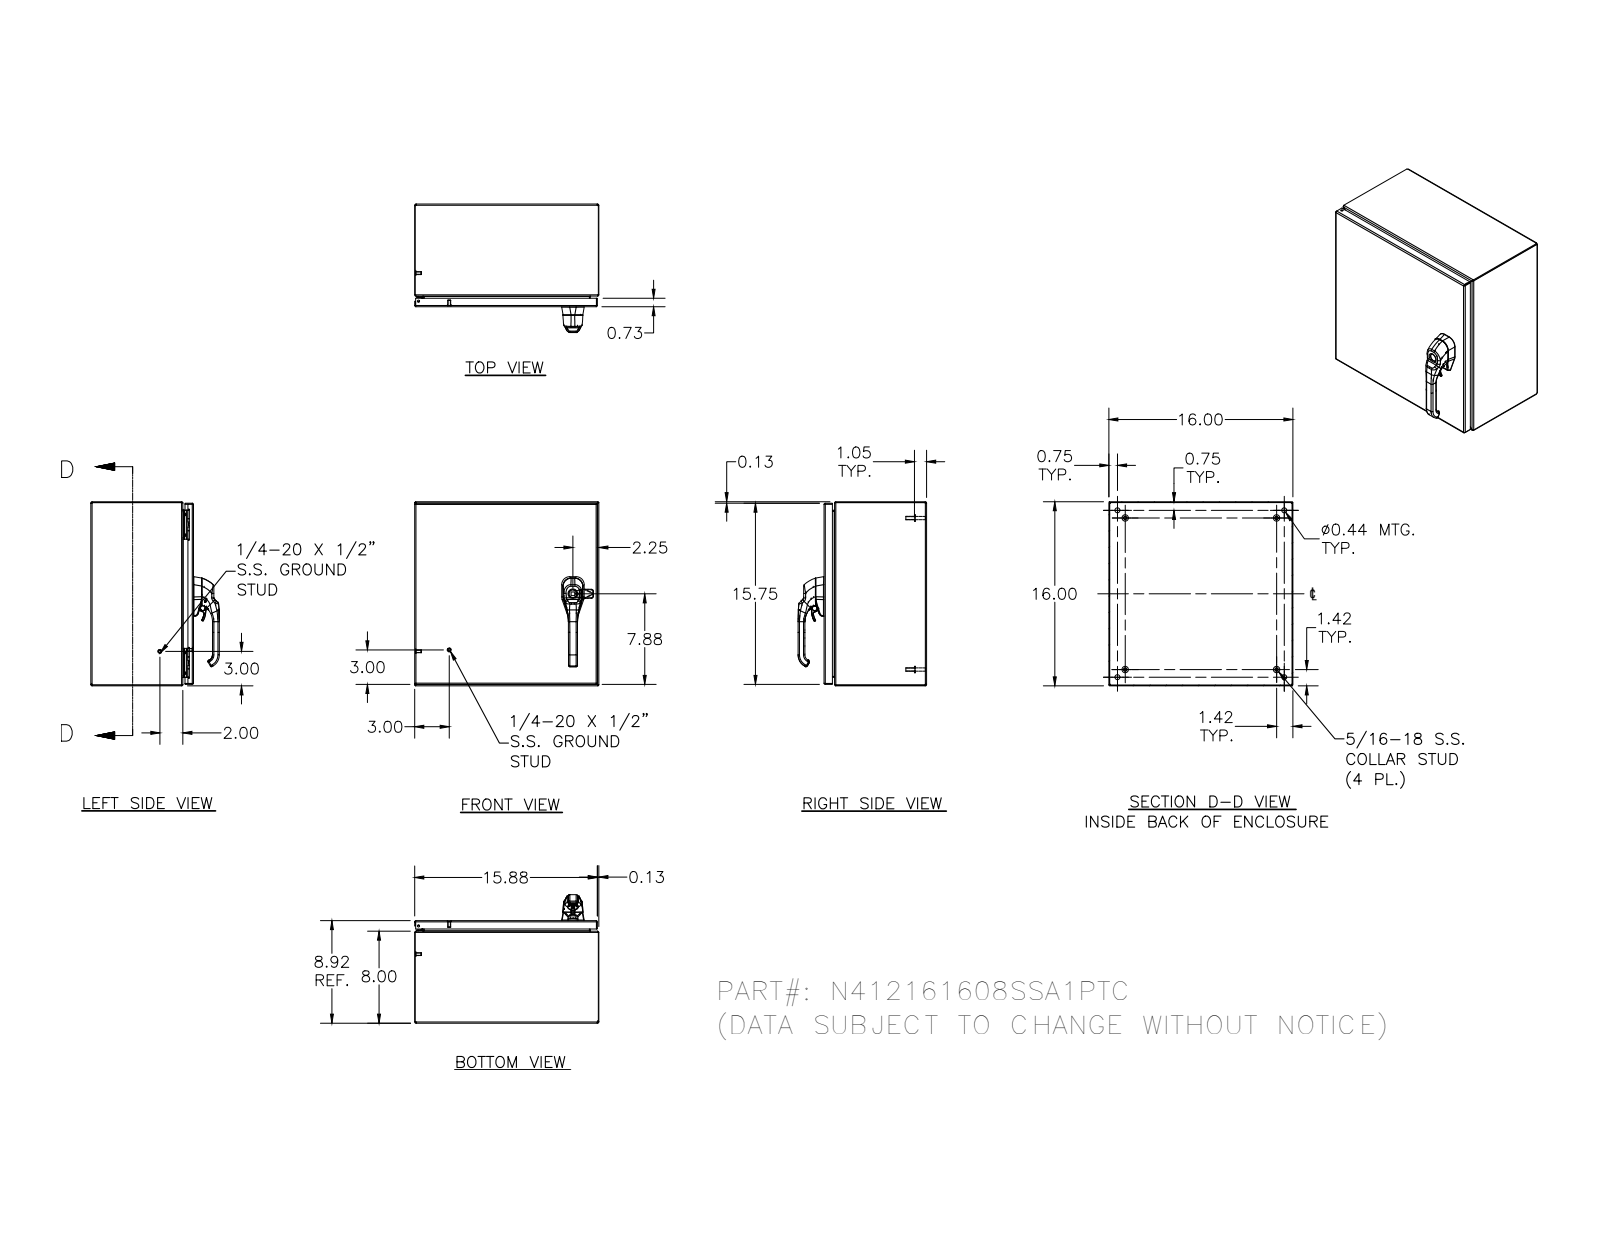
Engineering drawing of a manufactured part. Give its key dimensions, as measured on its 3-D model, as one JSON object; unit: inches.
{"part_name": "N412161608SSA1PTC; NA12161608SSA1PTCBKP; N4121616SSA1PTCLID; HFW328176 (+8 more)", "step_written_by": "Autodesk Inventor 2012 (AUTOMOTIVE_DESIGN)", "units": "inches", "bodies": {"solids": 41, "faces": 2784, "planar": 882, "cylindrical": 1037, "other": 865}, "overall_size": [16, 16, 11.166], "volume_in3": 92.7, "surface_area_in2": 2423, "round_holes": [[0.188, 5], [0.093, 4], [0.152, 4], [0.167, 4], [0.172, 4], [0.437, 4], [0.213, 3], [0.281, 3], [0.156, 2], [0.315, 2], [0.402, 2], [0.413, 2]], "round_bosses_or_shafts": [[0.25, 10], [0.563, 4], [0.36, 4], [0.32, 4], [0.3, 4], [0.275, 4], [0.256, 4], [0.164, 4]], "partial_cylinders_radius": [[0.02, 173], [0.012, 101], [0.031, 30], [0.05, 26], [0.019, 21], [0.105, 20], [0.016, 18], [0.079, 14]], "face_to_face_distances": [0.074, 15.926, 8.843, 16, 15.852, 8.917, 8.769, 7.926, 0.917, 0.125], "hole_center_spacings": [11.996, 14.5, 0.017, 0.66, 12.656, 14.181, 15.173, 0.019]}
